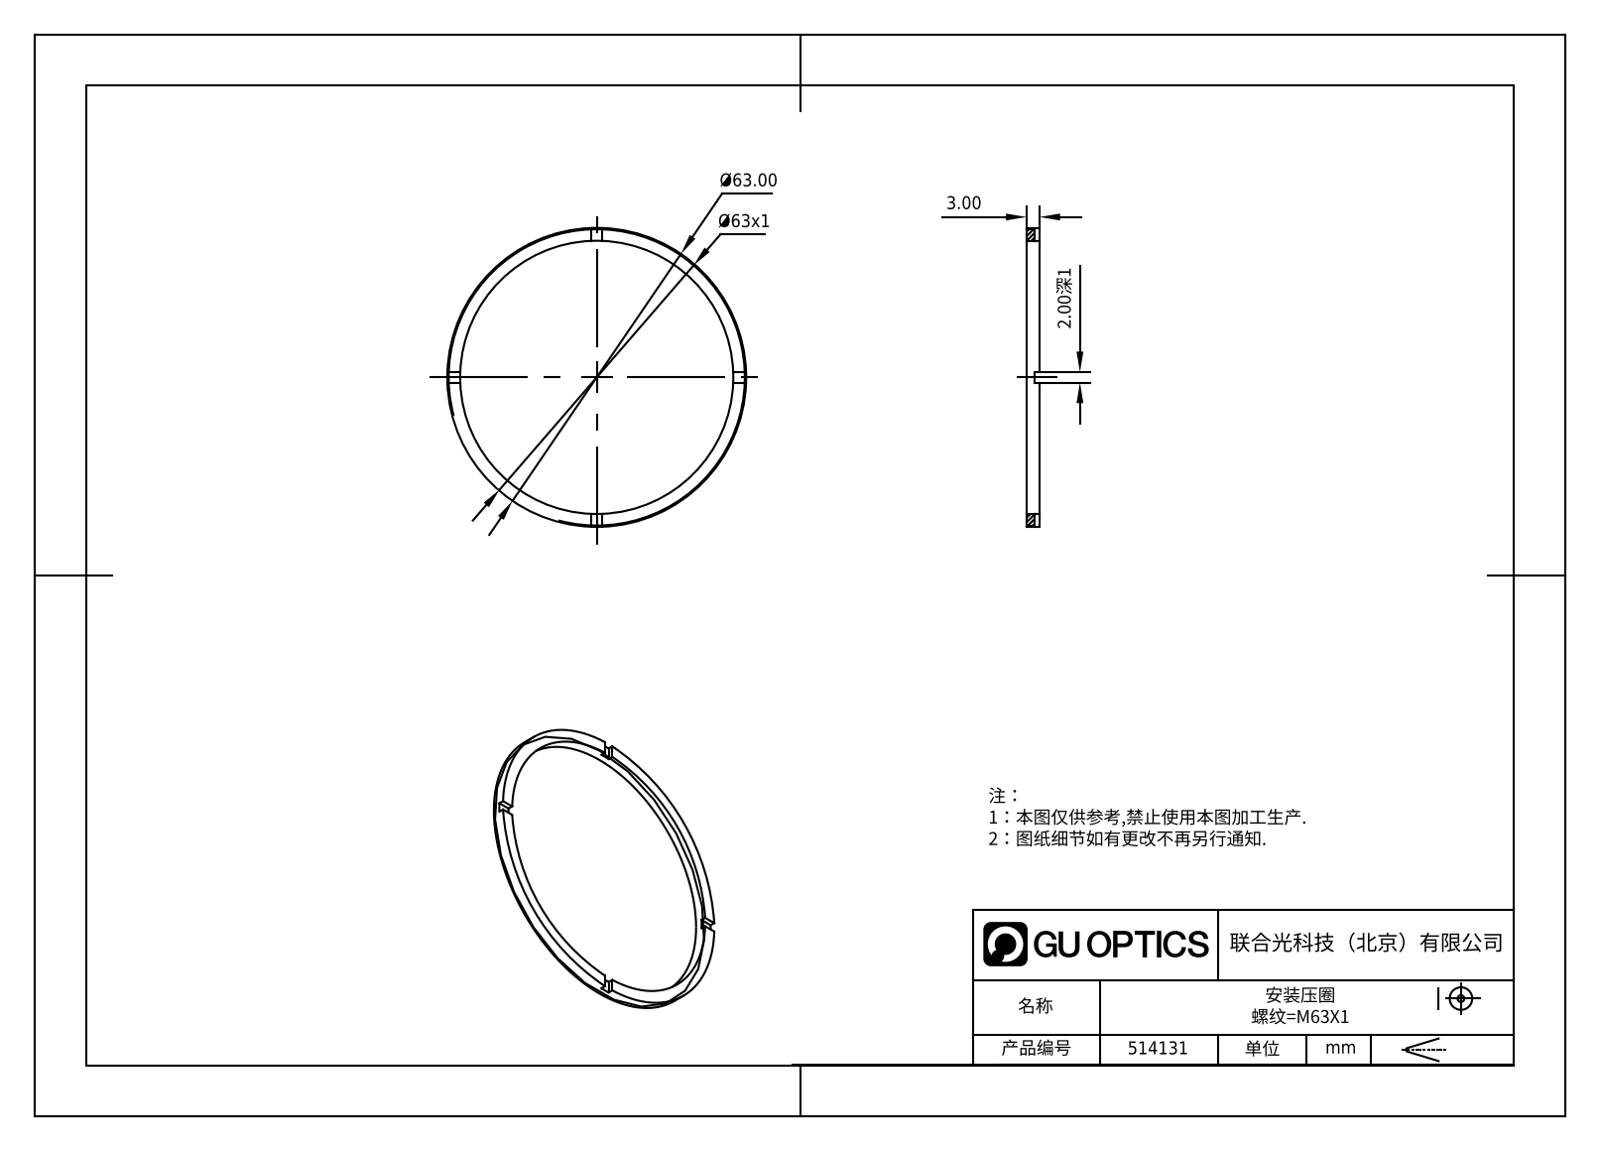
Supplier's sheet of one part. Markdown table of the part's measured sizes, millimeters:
| quantity | value |
| --- | --- |
| part name | 514131 |
| STEP written by | SolidWorks 2020 (CONFIG_CONTROL_DESIGN) |
| units | millimeters |
| bodies | 1 solid, 21 faces (17 planar, 4 cylindrical, 0 other) |
| overall size | 63 × 63 × 3 |
| volume | 1 405 mm³ |
| surface area | 2 095 mm² |
| round holes (diameter × count) | 58 × 1 |
| round bosses / shafts (diameter × count) | 63 × 1 |
| main face-to-face distances | 3, 2, 1 |
